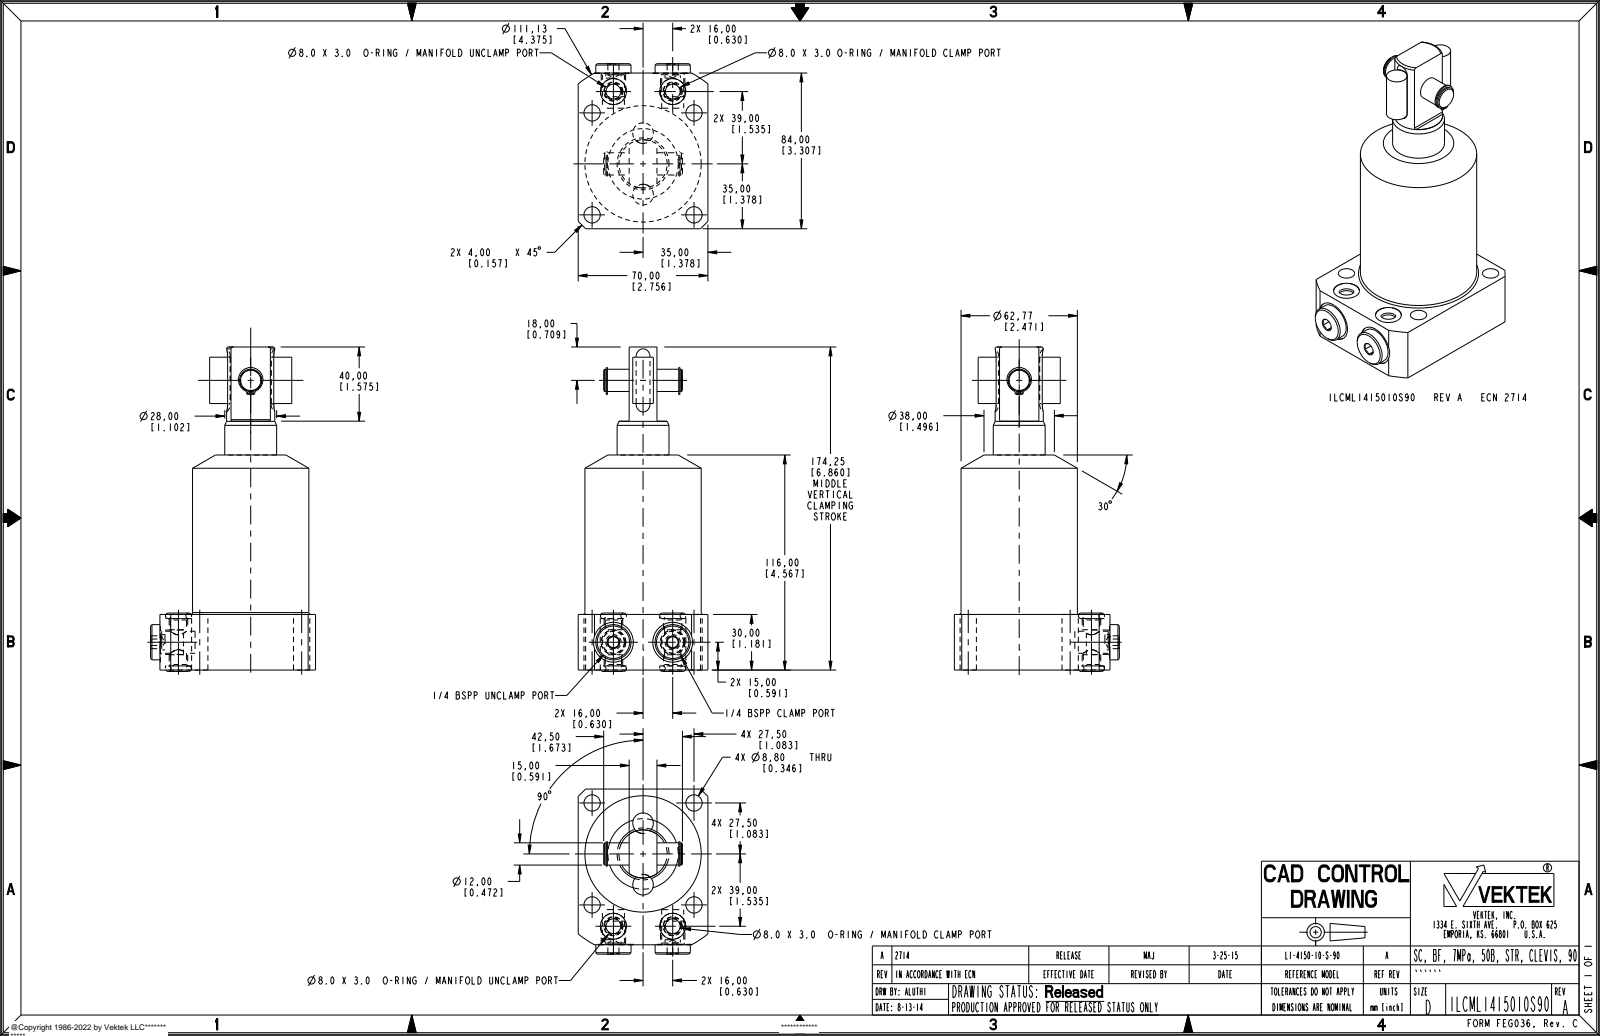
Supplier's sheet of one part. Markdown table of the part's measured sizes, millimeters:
| quantity | value |
| --- | --- |
| part name | ILCML1415010S90 |
| STEP written by | PRO/ENGINEER BY PARAMETRIC TECHNOLOGY CORPORATION, 2013320 (AUTOMOTIVE_DESIGN) |
| units | millimeters |
| bodies | 7 solids, 240 faces (80 planar, 96 cylindrical, 64 other) |
| overall size | 175 × 89.05 × 70 |
| volume | 455 252 mm³ |
| surface area | 53 785 mm² |
| round holes (diameter × count) | 8.8 × 4, 1.04 × 2, 8.75 × 2, 11.89 × 2, 14 × 2, 21.5 × 2 |
| round bosses / shafts (diameter × count) | 19 × 2, 13.16 × 2, 11.12 × 2, 10 × 2, 8.25 × 2, 62.77 × 1, 28 × 1, 26 × 1 |
| partial cylindrical surfaces (radius × count) | 0.8 × 2, 1.04 × 2, 1.09 × 2, 5.56 × 2, 55.56 × 1 |
| main face-to-face distances | 70, 30, 42.5, 27.5, 84, 15, 116, 86, 27.75, 89.05 |
| hole center spacings | 55, 16.26, 32, 44.99, 67.49, 77.78, 79.46, 2.4 |
